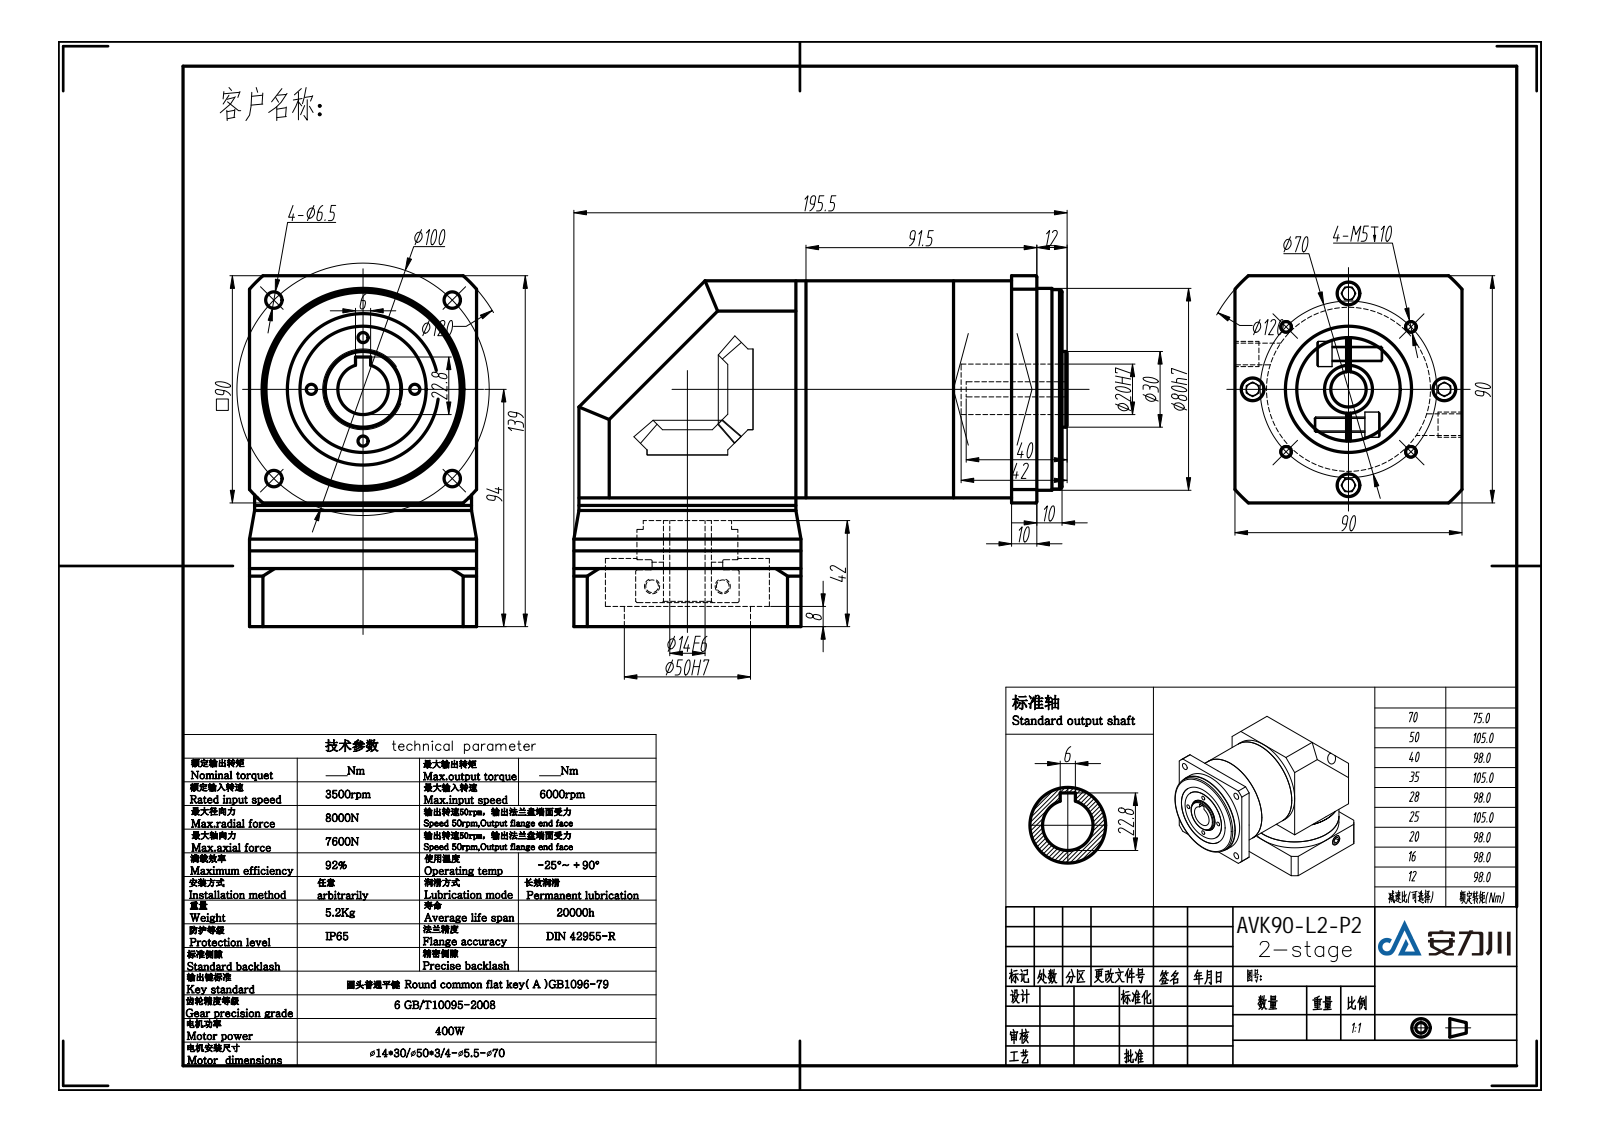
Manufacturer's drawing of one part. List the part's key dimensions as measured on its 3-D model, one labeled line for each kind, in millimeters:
Part name (STEP PRODUCT): VGZK85双级模型（14-30 50-3 4-5.5-70）
STEP written by: SolidWorks 2016 (AUTOMOTIVE_DESIGN)
Units: millimetres
Bodies: 6 solids, 340 faces (191 planar, 131 cylindrical, 18 other)
Overall size (bounding box): 195.5 × 139 × 90
Volume: 1 388 000 mm³ · Surface area: 171 269 mm²
Round holes (diameter × count): ⌀10 ×8, ⌀4 ×4, ⌀4.2 ×4, ⌀6.5 ×4, ⌀9 ×4, ⌀20 ×2, ⌀14 ×1, ⌀19 ×1, ⌀32.2 ×1, ⌀50 ×1, ⌀60 ×1, ⌀65 ×1
Round bosses / shafts (diameter × count): ⌀8.5 ×6, ⌀8.4 ×4, ⌀86 ×2, ⌀9.8 ×2, ⌀90 ×1, ⌀80 ×1, ⌀79 ×1, ⌀50 ×1
Partial cylindrical surfaces — rounded edges, fillets, slot ends (radius × count): R60 ×2
Main face-to-face distances: 2, 18, 58.5, 88, 86, 90, 48, 30, 10, 21
Hole centre spacings: 38, 28.07, 38.36, 53.74, 66.11, 67.45, 20.61, 20.82
